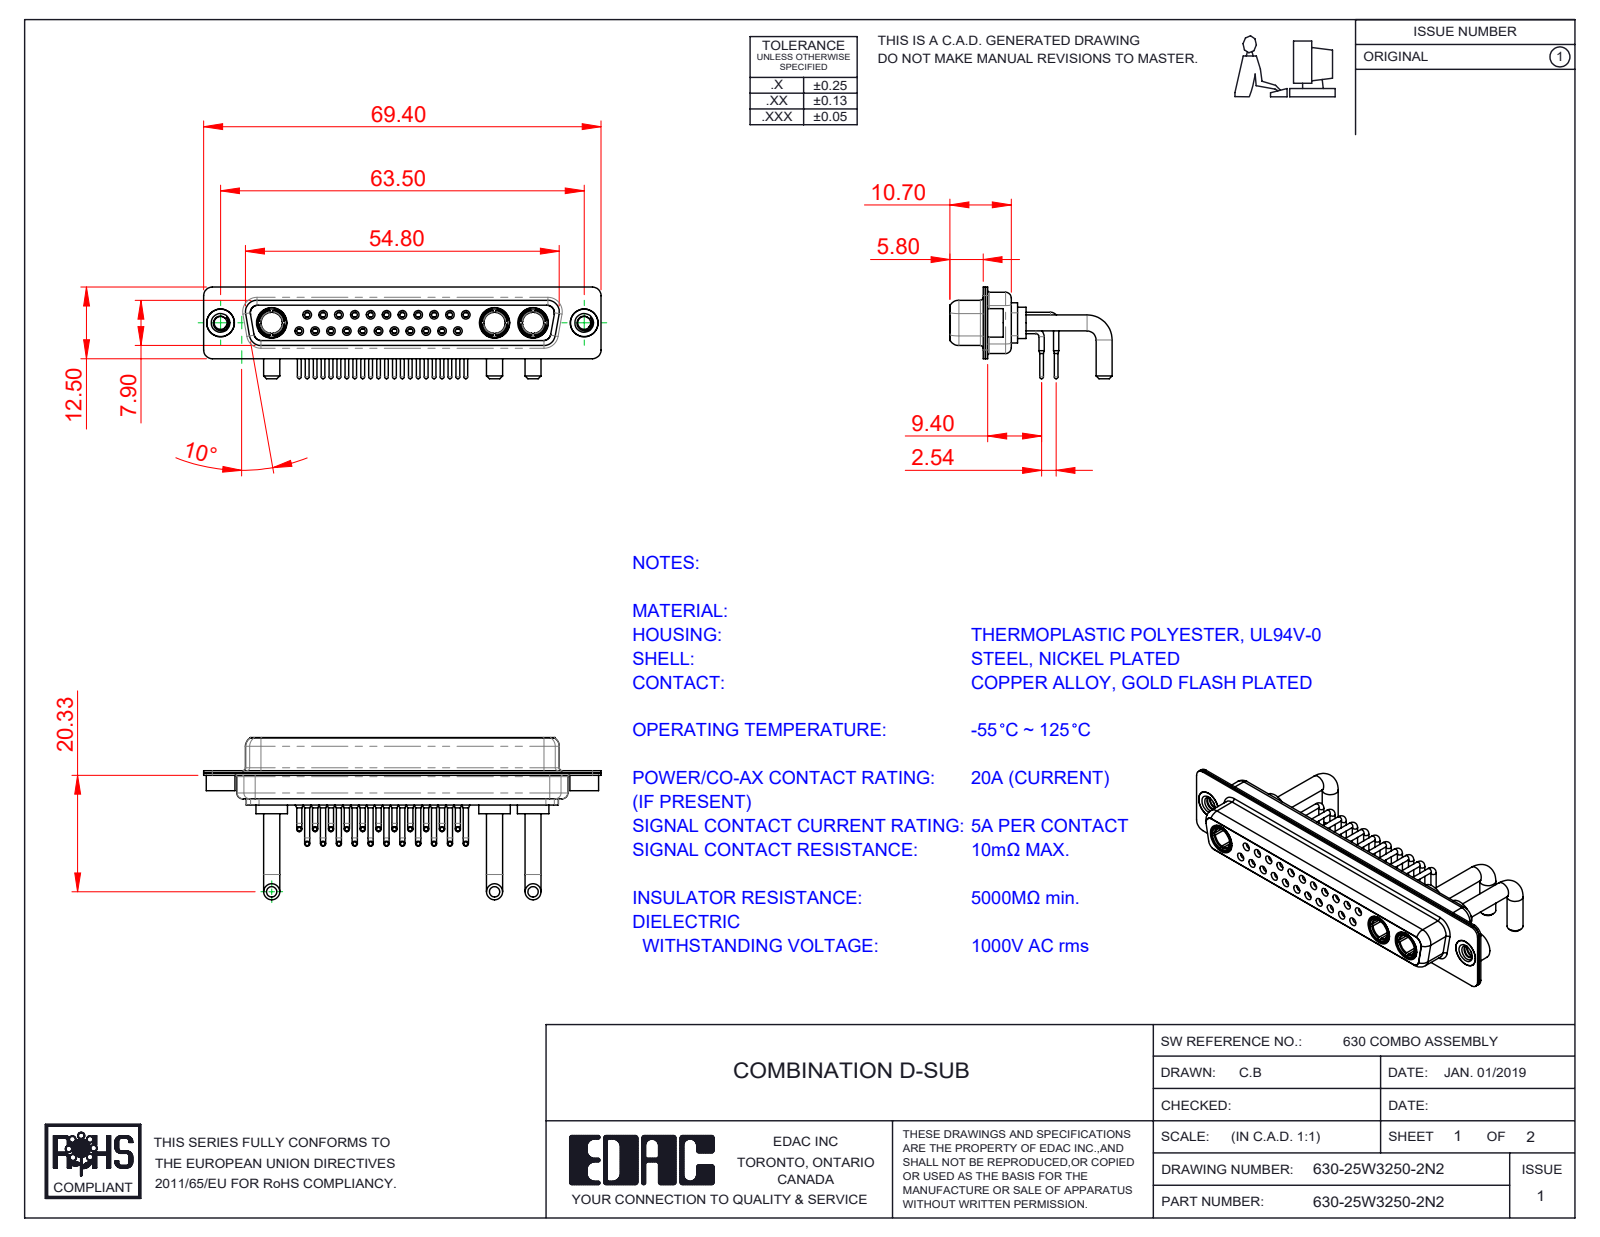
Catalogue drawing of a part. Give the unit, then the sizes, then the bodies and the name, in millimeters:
Units: millimetres
Overall size (bounding box): 69.4 × 28.33 × 16
Round holes (diameter × count): ⌀0.9 ×22, ⌀1.1 ×22, ⌀1.5 ×22, ⌀2 ×22, ⌀1.6 ×11, ⌀1.7 ×11, ⌀4.85 ×5, ⌀3.7 ×3, ⌀5.3 ×3, ⌀2.26 ×2, ⌀4 ×2, ⌀4.05 ×2
Round bosses / shafts (diameter × count): ⌀0.9 ×23, ⌀0.65 ×22, ⌀1.6 ×12, ⌀2.8 ×6, ⌀5.5 ×3, ⌀5.2 ×3, ⌀4.96 ×3, ⌀4.75 ×3
Partial cylindrical surfaces — rounded edges, fillets, slot ends (radius × count): R1.5 ×16, R2 ×12, R1.35 ×8, R1.6 ×8, R0.25 ×4, R0.5 ×4, R0.6 ×4, R0.65 ×4
Main face-to-face distances: 0.4, 1.4, 0.45, 8.45, 1.8, 8.9, 6.2, 7.05, 1.85, 7.5
Hole centre spacings: 3.16, 2.77, 5.54, 5.03, 8.31, 7.48, 11.08, 5.04
Volume: 5 808 mm³ · Surface area: 12 904 mm²
Bodies: 33 solids, 1679 faces (484 planar, 718 cylindrical, 477 other)
Part name (STEP PRODUCT): 630Combo Housing_25W3; 630Combo Shell Front_37 Contacts; 630Combo Contact Row 2; 630Combo Shell Rear_37 Contacts (+4 more)
STEP written by: SolidWorks 2020 (CONFIG_CONTROL_DESIGN)
